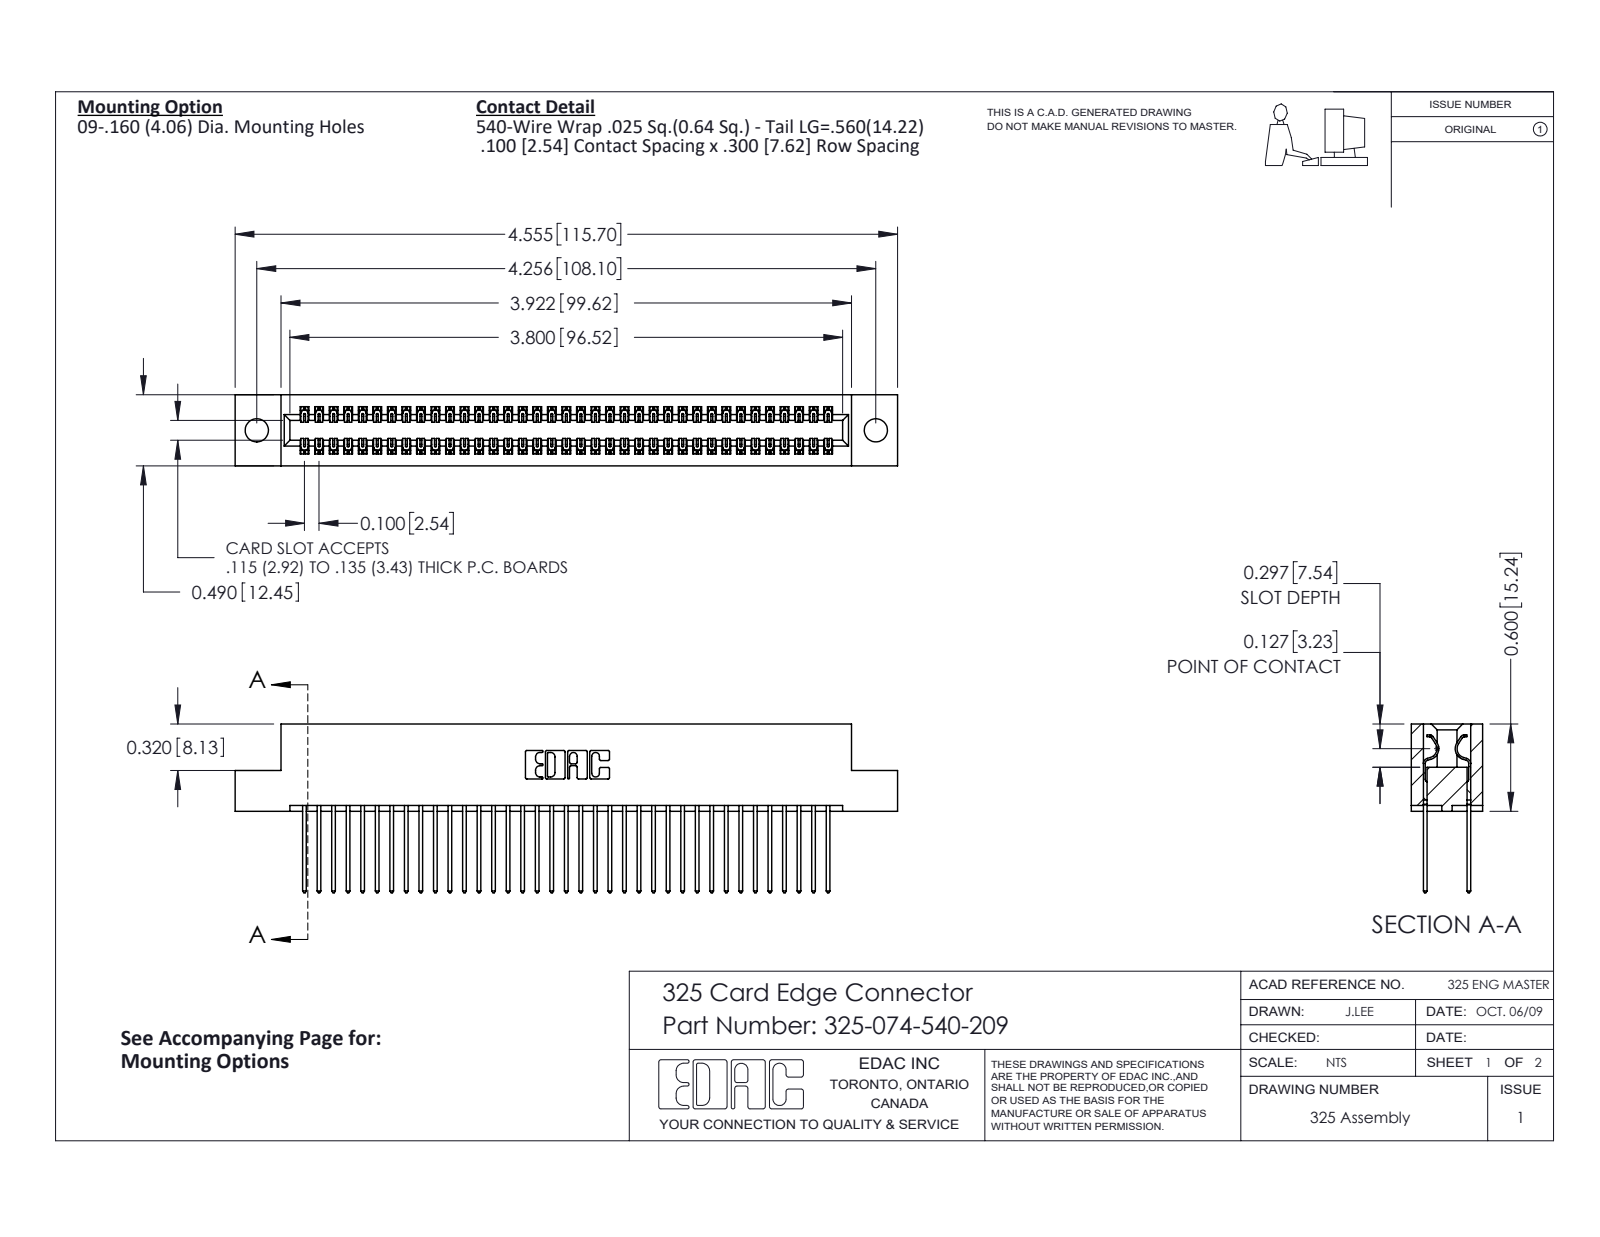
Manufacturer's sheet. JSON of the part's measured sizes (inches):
{"part_name": "325 Part_.160 TH; 325-074-540-209; 325-292-001_325-293-140", "step_written_by": "SolidWorks 2016 (CONFIG_CONTROL_DESIGN)", "units": "inches", "bodies": {"solids": 75, "faces": 3962, "planar": 2734, "cylindrical": 1228, "other": 0}, "overall_size": [4.555, 1.16, 0.49], "volume_in3": 0.912, "surface_area_in2": 29.79, "round_holes": [[0.16, 2]], "partial_cylinders_radius": [[0.006, 111], [0.01, 74], [0.01, 22], [0.007, 6], [0.031, 6], [0.026, 3], [0.014, 2], [0.022, 2]], "face_to_face_distances": [0.083, 0.407, 0.3, 0.107, 0.383, 0.025, 0.49, 0.325, 0.275, 0.56], "hole_center_spacings": [4.256]}
